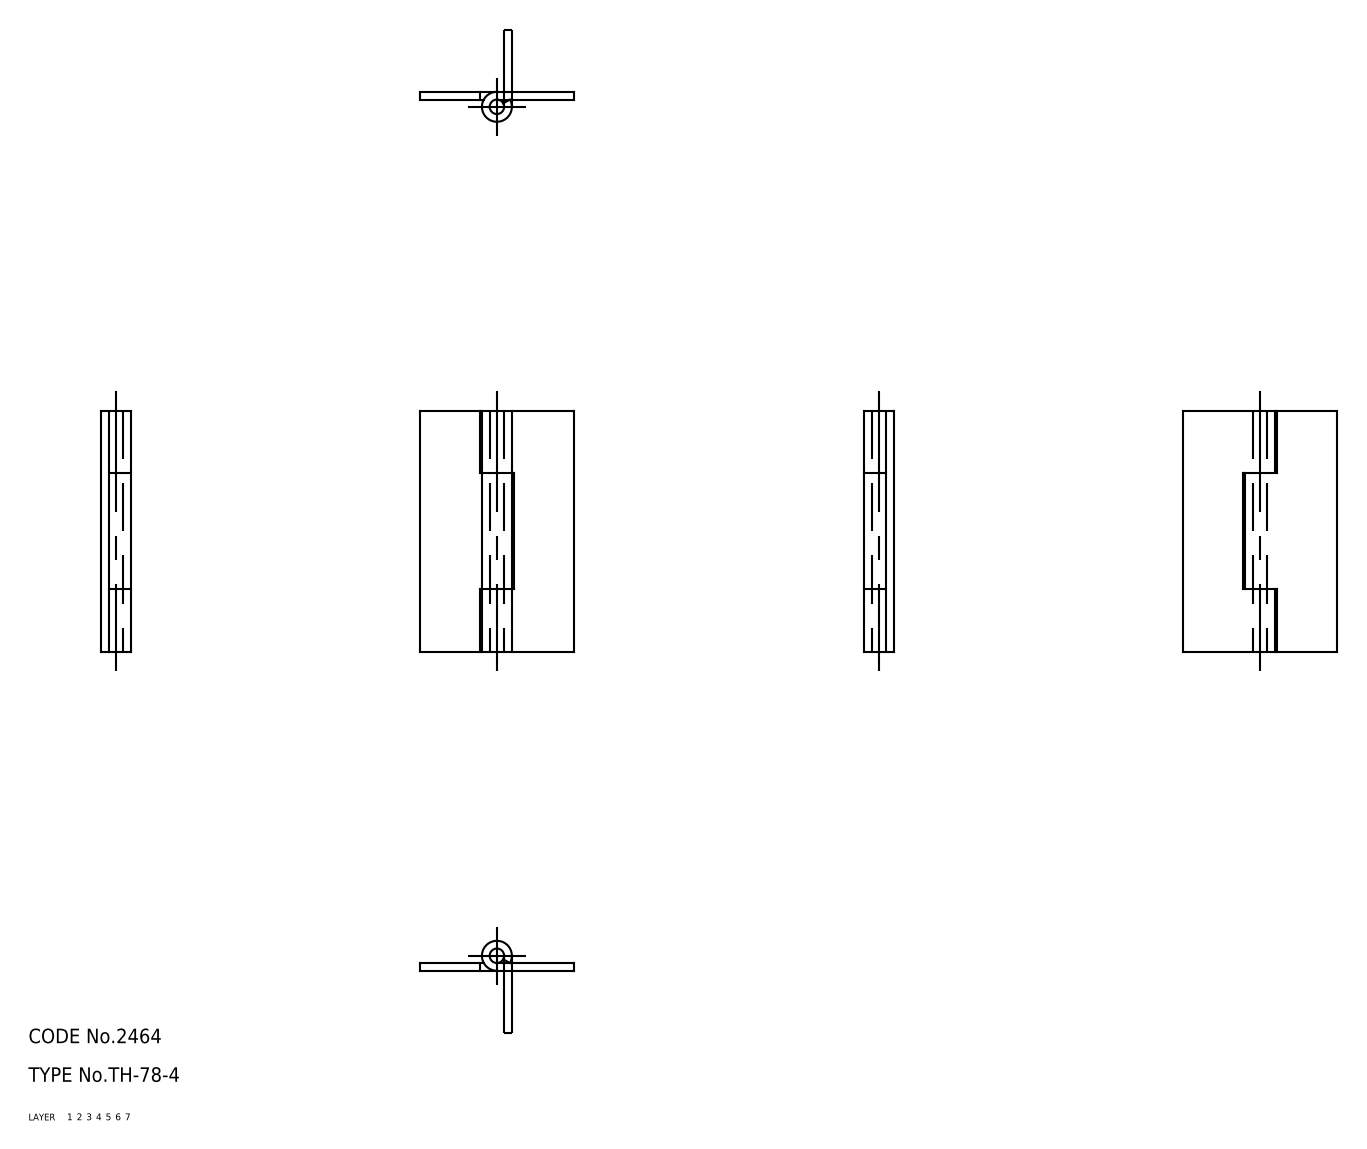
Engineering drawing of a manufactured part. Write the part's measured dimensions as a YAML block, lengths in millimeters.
part_name: "hinge piece_B; hinge piece_A; shaft; TH_78_4_16720_36"
step_written_by: "CADfix (AUTOMOTIVE_DESIGN)"
units: millimeters
bodies: {solids: 3, faces: 30, planar: 0, cylindrical: 0, other: 30}
overall_size: [50, 32, 6.2]
volume: 3591
surface_area: 5080
